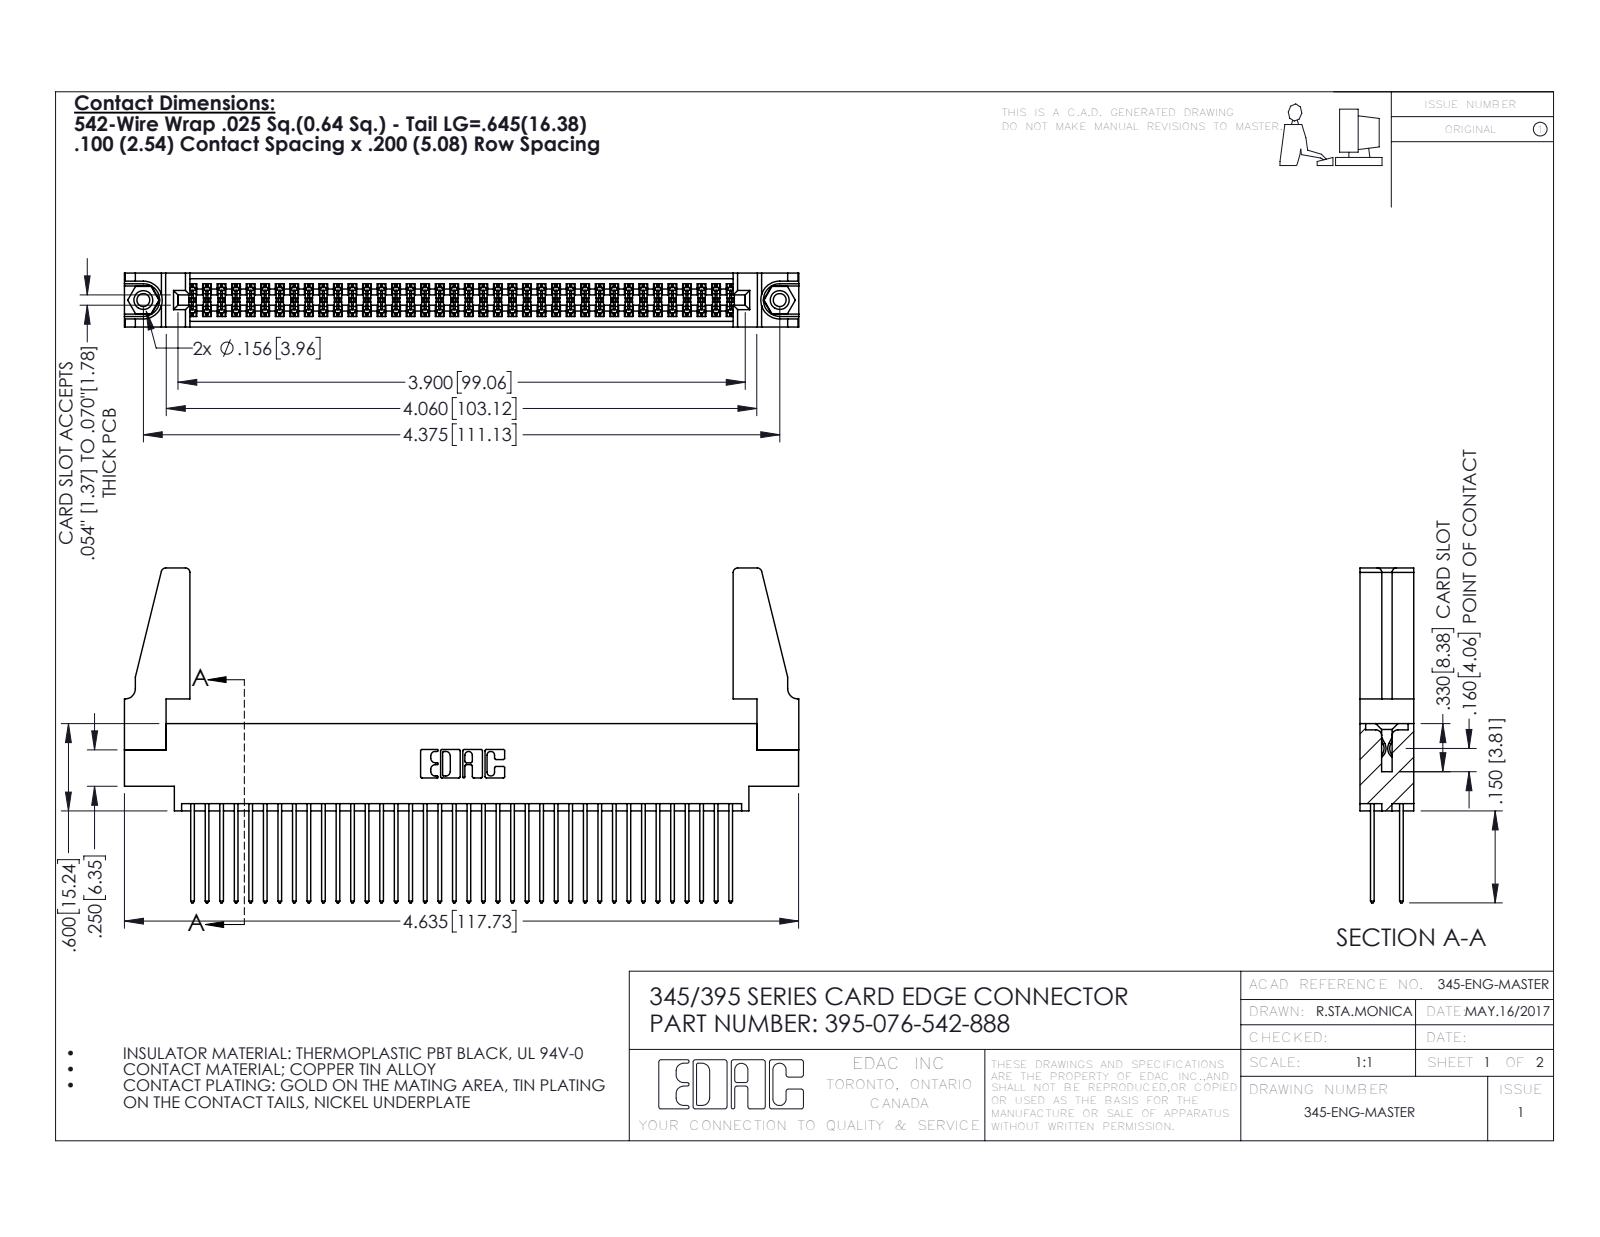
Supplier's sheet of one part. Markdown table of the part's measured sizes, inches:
| quantity | value |
| --- | --- |
| part name | 345-220-078_345-220-088; 345 Part_0.170 Offset - 0.156 Dia-TH; 395-076-542-888; 345-292-001_345-293-142 (+1 more) |
| STEP written by | SolidWorks 2016 (CONFIG_CONTROL_DESIGN) |
| units | inches |
| bodies | 81 solids, 4054 faces (2664 planar, 1374 cylindrical, 16 other) |
| overall size | 4.636 × 2.302 × 0.37 |
| volume | 0.909 in³ |
| surface area | 34.18 in² |
| round holes (diameter × count) | 0.089 × 2, 0.125 × 2, 0.156 × 2, 0.064 × 1 |
| round bosses / shafts (diameter × count) | 0.155 × 2 |
| partial cylindrical surfaces (radius × count) | 0.006 × 114, 0.01 × 76, 0.01 × 22, 0.03 × 8, 0.007 × 6, 0.031 × 6, 0.026 × 3, 0.014 × 2 |
| main face-to-face distances | 0.072, 0.298, 0.37, 0.2, 0.098, 0.272, 0.025, 0.225, 0.175, 0.149 |
| hole center spacings | 0.27, 4.139, 4.375 |
